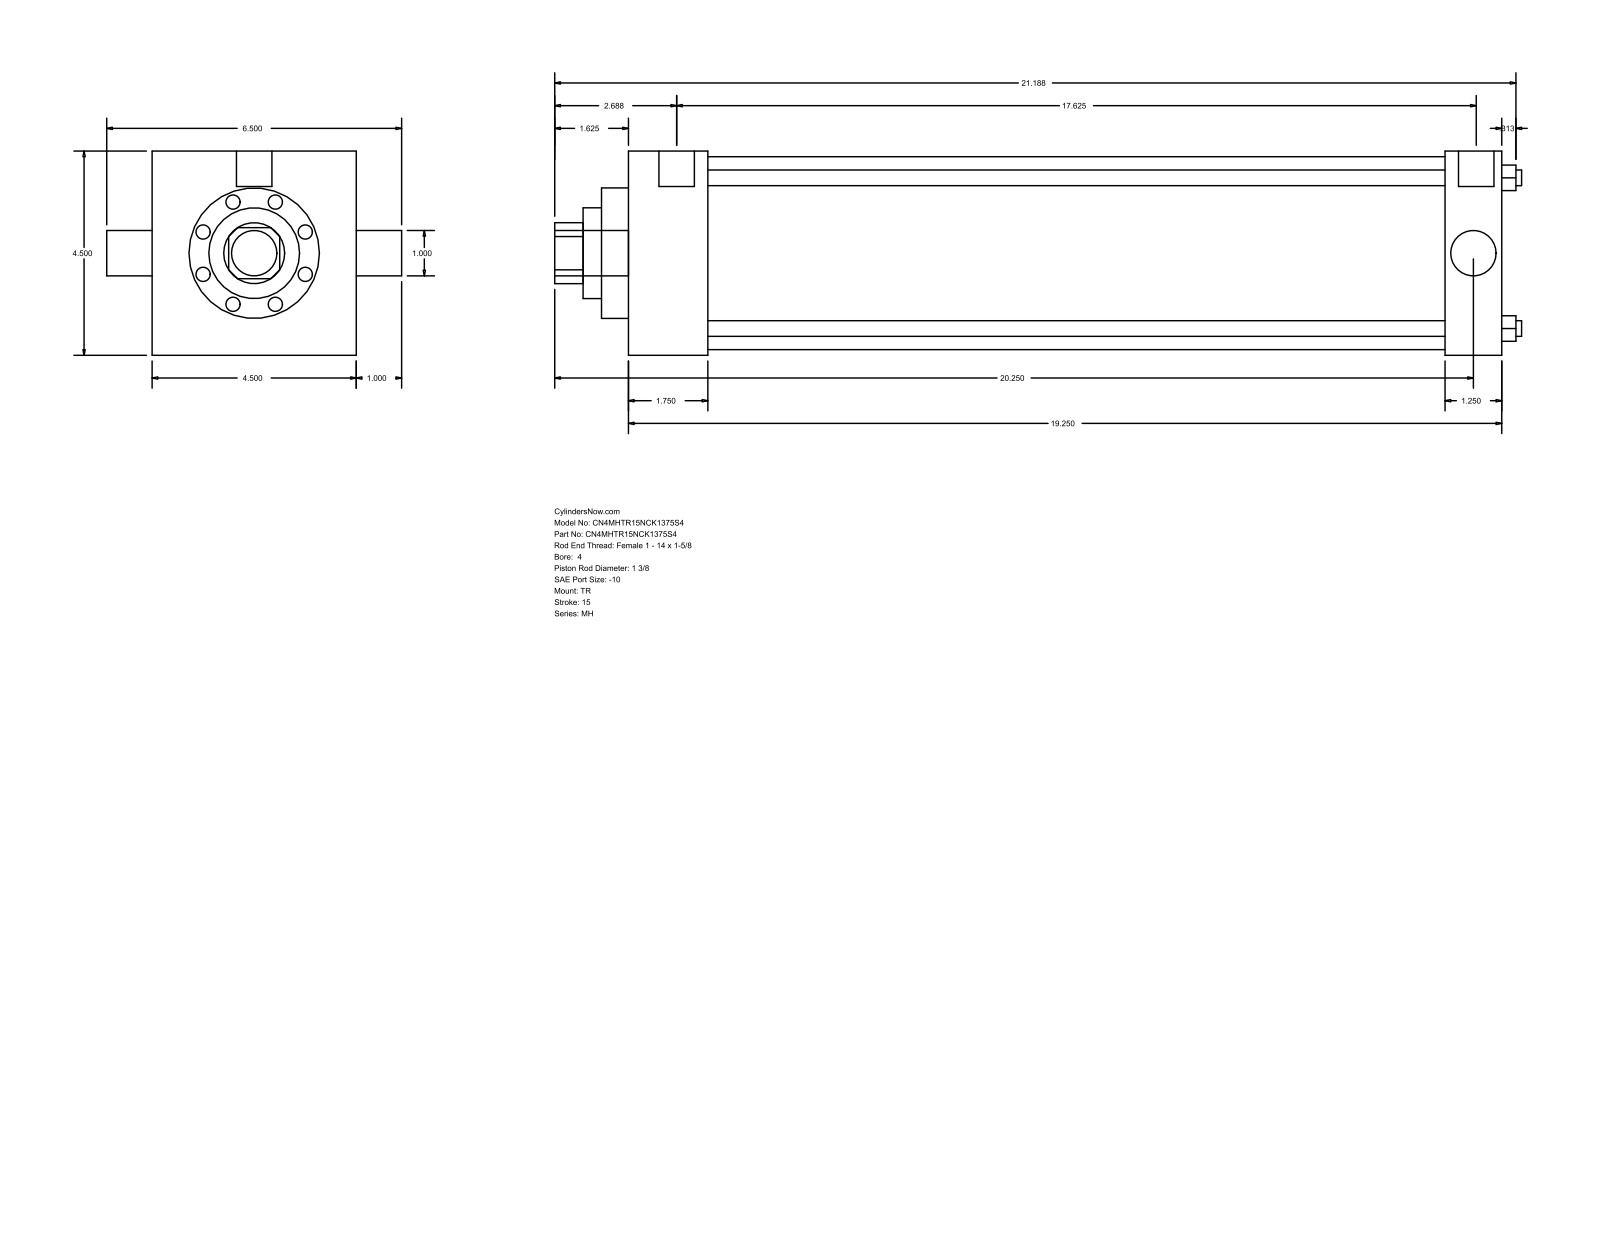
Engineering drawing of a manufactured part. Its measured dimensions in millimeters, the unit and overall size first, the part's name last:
Units: millimetres
Overall size (bounding box): 541.34 × 165.1 × 114.3
Round holes (diameter × count): ⌀8.76 ×4, ⌀25.4 ×1, ⌀34.92 ×1, ⌀50.8 ×1, ⌀73.03 ×1, ⌀107.95 ×1
Round bosses / shafts (diameter × count): ⌀8.73 ×3, ⌀19.84 ×2, ⌀25.4 ×1
Partial cylindrical surfaces — rounded edges, fillets, slot ends (radius × count): R17.06 ×1
Main face-to-face distances: 114.3, 488.96, 44.45, 444.51, 457.21, 412.76, 31.75, 15.08, 59.53, 472.29
Hole centre spacings: 59.62, 84.32, 119.25
Bodies: 0 solids, 86 faces (61 planar, 25 cylindrical, 0 other)
Part name (STEP PRODUCT): MH_TR__0400_1.375
STEP written by: GSSL Pune (CONFIG_CONTROL_DESIGN)
